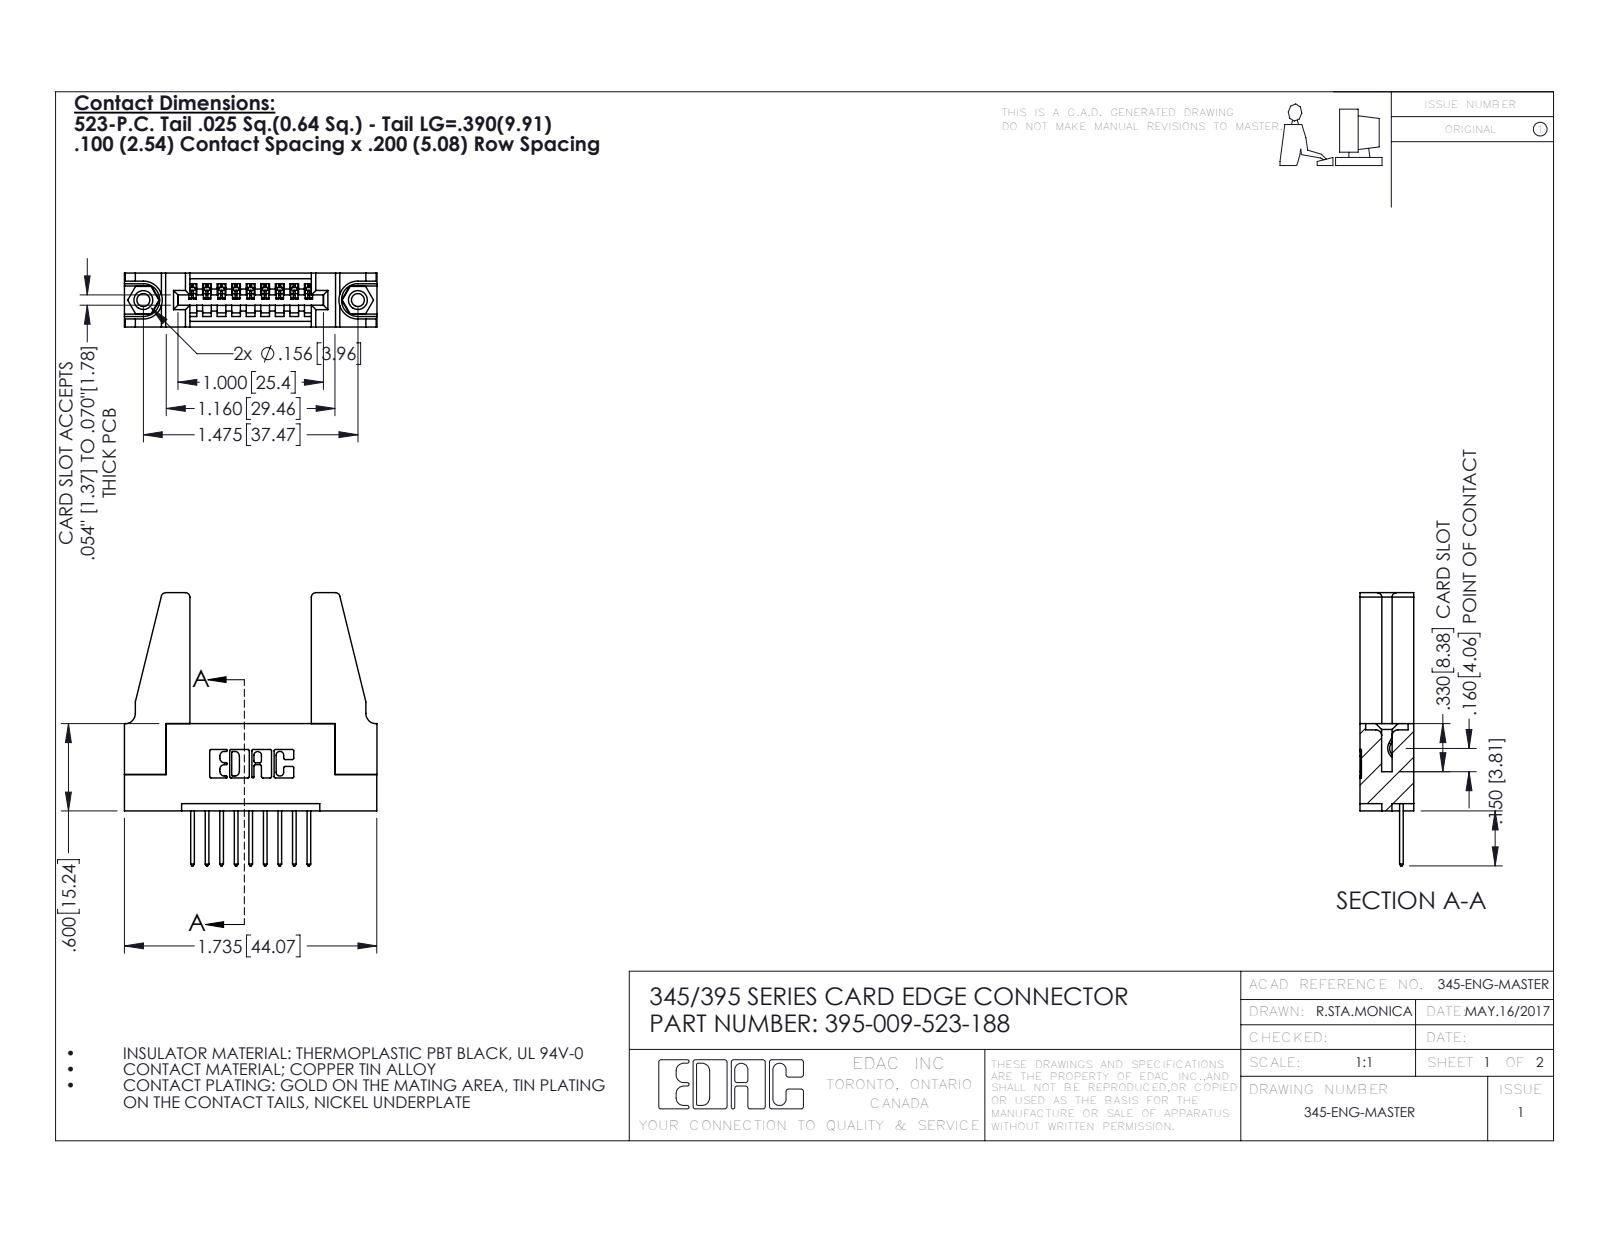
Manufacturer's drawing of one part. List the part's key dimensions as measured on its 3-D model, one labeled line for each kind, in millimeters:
Part name (STEP PRODUCT): 345-292-001_345-293-123; 345-220-078_345-220-088; 395-009-523-188; 345-250-001_345-250-001-102 (+1 more)
STEP written by: SolidWorks 2016 (CONFIG_CONTROL_DESIGN)
Units: millimetres
Bodies: 14 solids, 772 faces (512 planar, 244 cylindrical, 16 other)
Overall size (bounding box): 47.7 × 44.1 × 9.4
Volume: 7 160 mm³ · Surface area: 7 890 mm²
Round holes (diameter × count): ⌀2.3 ×2, ⌀3.2 ×2, ⌀4 ×2, ⌀1.6 ×1
Round bosses / shafts (diameter × count): ⌀3.9 ×2
Partial cylindrical surfaces — rounded edges, fillets, slot ends (radius × count): R0.3 ×22, R0.2 ×18, R0.3 ×18, R0.8 ×8, R0.2 ×6, R0.8 ×6, R0.7 ×3, R0.8 ×2
Main face-to-face distances: 9.4, 1.8, 7.6, 5.1, 2.5, 6.9, 0.6, 3.8, 3.8, 6.4
Hole centre spacings: 6.9, 31.6, 37.5
